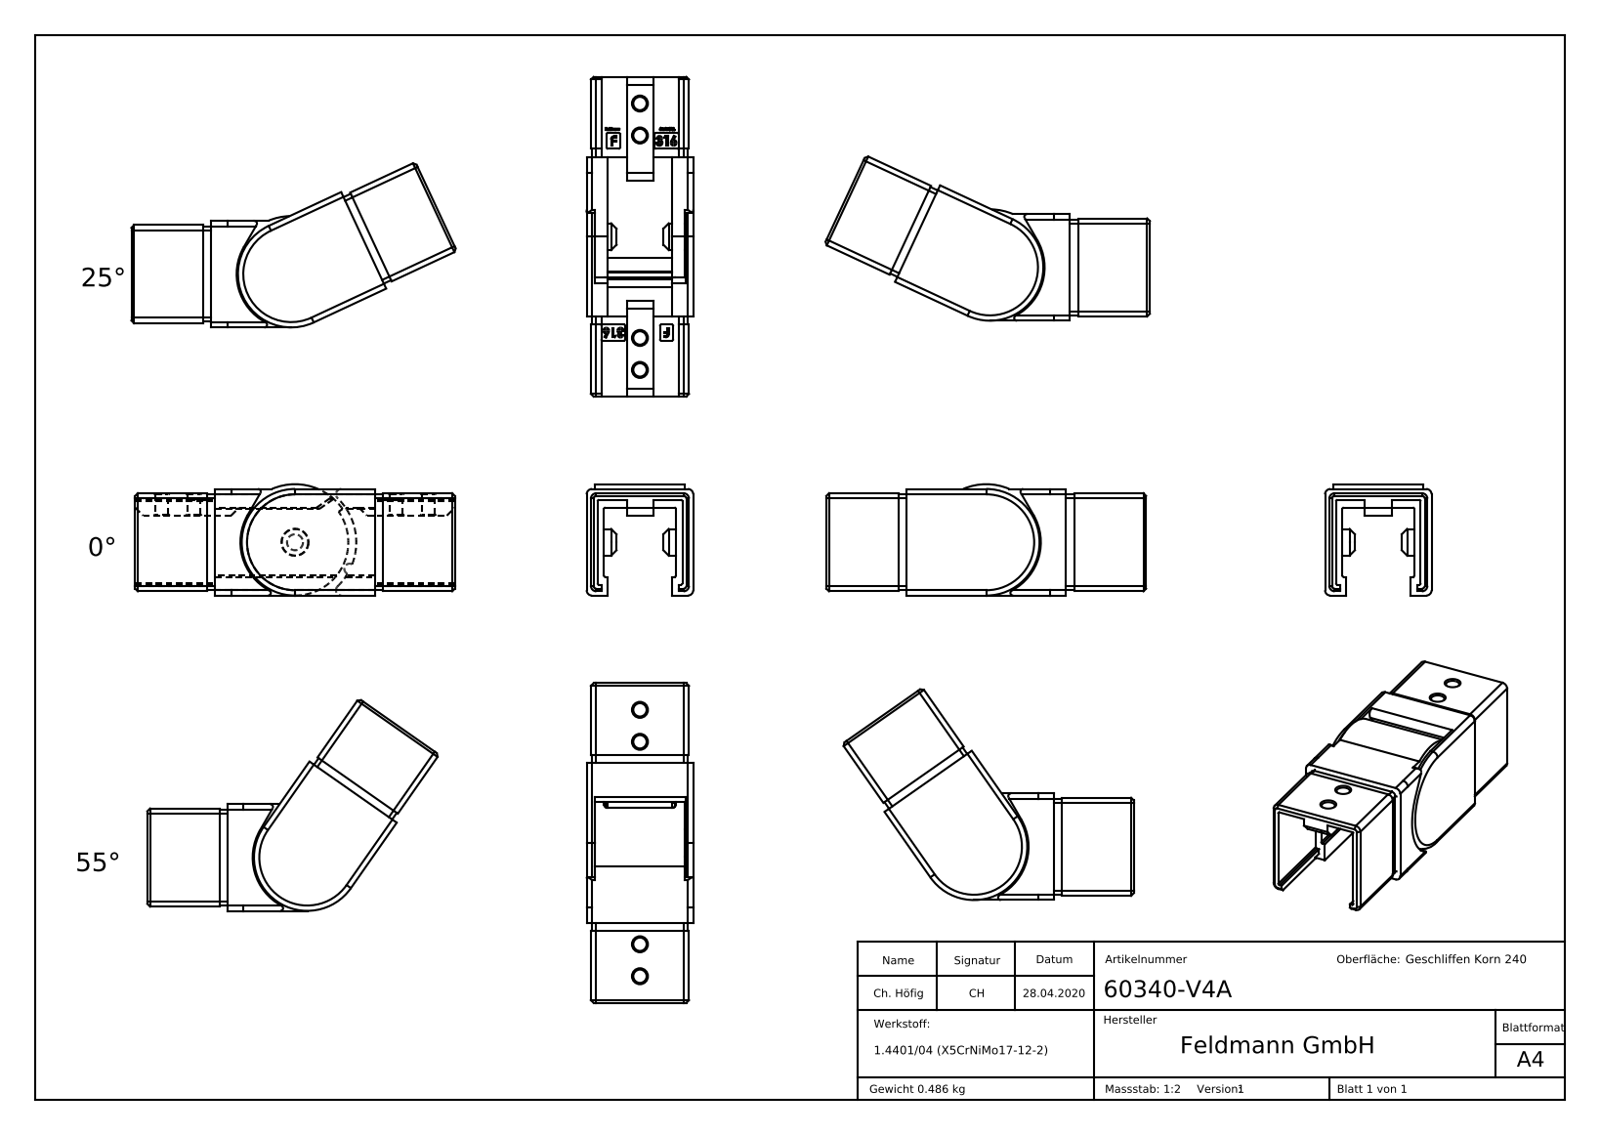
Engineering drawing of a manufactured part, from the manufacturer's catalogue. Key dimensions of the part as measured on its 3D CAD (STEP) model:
Part name (STEP PRODUCT): 60340-V4A Teil2; 60340-V4A Teil2_60340-V4A Teil2; 60340-V4A Teil1; 60340-V4A (+1 more)
STEP written by: SolidWorks 2015 (CONFIG_CONTROL_DESIGN)
Units: millimetres
Bodies: 2 solids, 570 faces (321 planar, 92 cylindrical, 157 other)
Overall size (bounding box): 120 × 41.8 × 40
Volume: 60 760 mm³ · Surface area: 36 040 mm²
Round holes (diameter × count): ⌀5 ×4, ⌀10.1 ×1
Round bosses / shafts (diameter × count): ⌀40 ×1, ⌀10 ×1
Partial cylindrical surfaces — rounded edges, fillets, slot ends (radius × count): R0.5 ×25, R2 ×11, R1 ×4, R1.5 ×4, R20.5 ×1, R21.8 ×1, R23 ×1
Main face-to-face distances: 2.5, 4.1, 1.6, 35.9, 38.4, 34.3, 3, 32.9, 1.4, 4.9
Hole centre spacings: 12, 88, 76, 100
